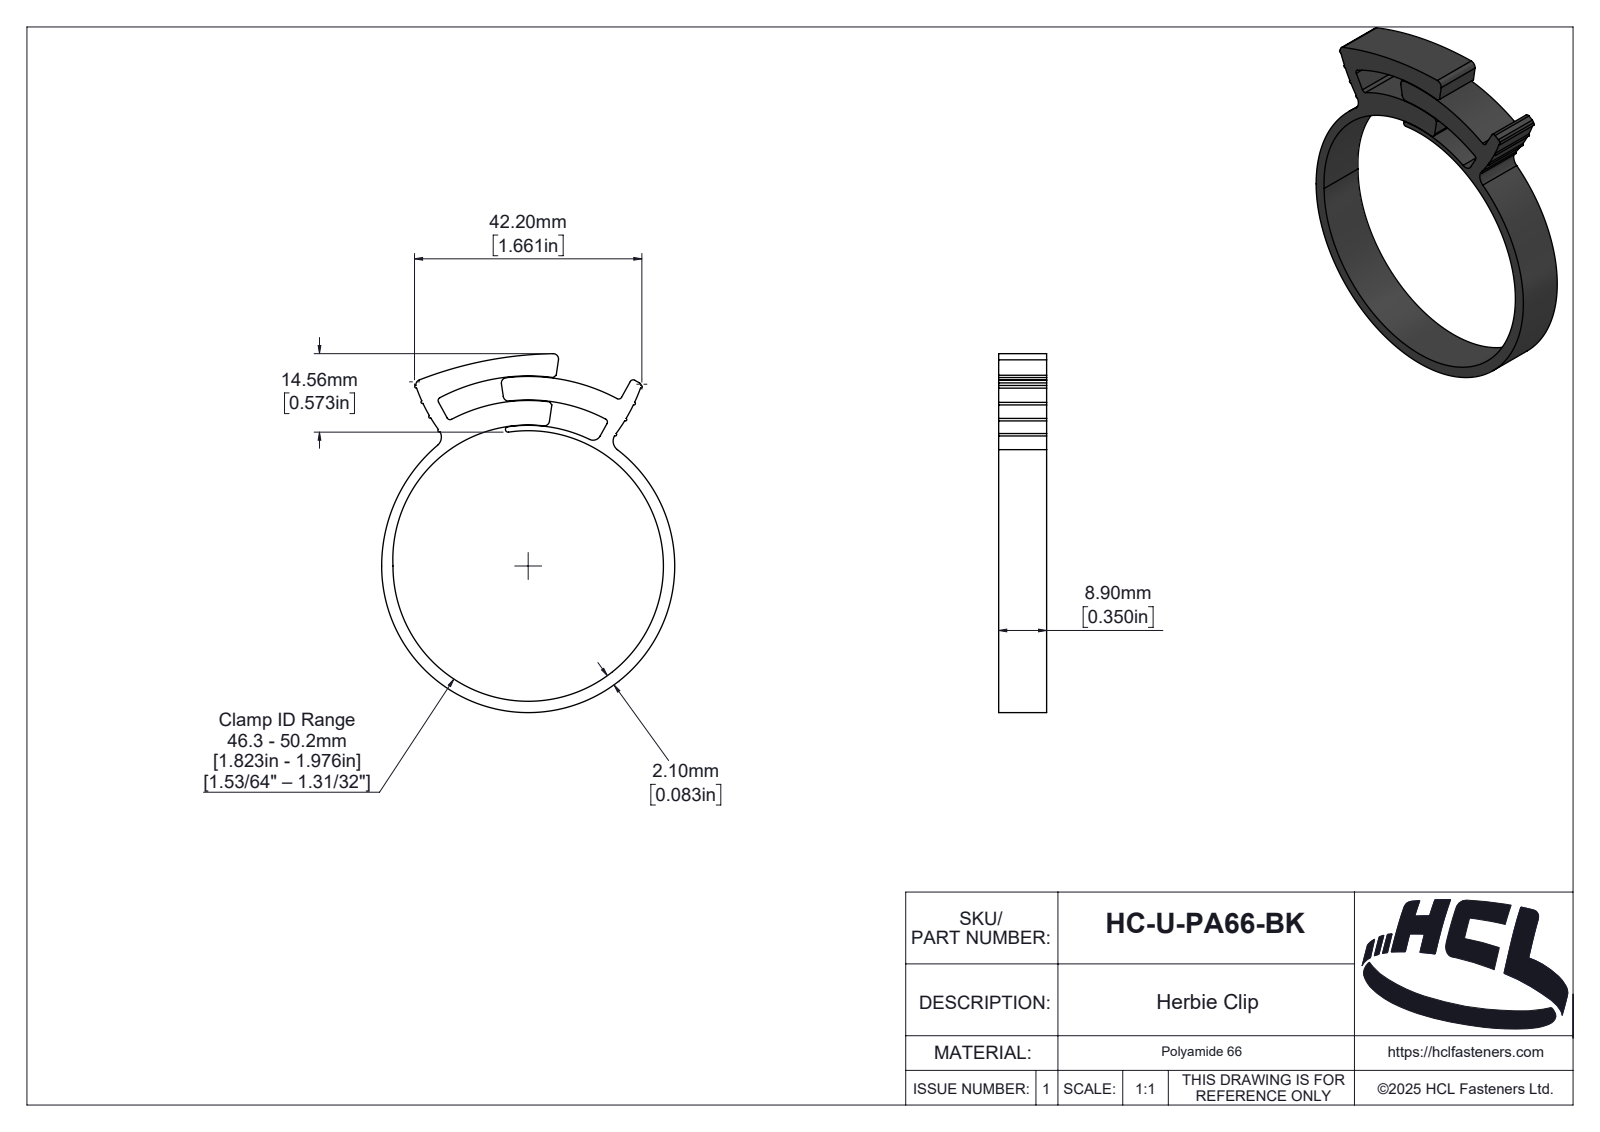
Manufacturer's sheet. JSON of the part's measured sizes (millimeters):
{"part_name": "HC-U-PA66-BK", "step_written_by": "SolidWorks 2025 (AUTOMOTIVE_DESIGN)", "units": "millimeters", "bodies": {"solids": 1, "faces": 162, "planar": 13, "cylindrical": 100, "other": 49}, "overall_size": [66.59, 54.4, 8.9], "volume_mm3": 5670, "surface_area_mm2": 5619, "partial_cylinders_radius": [[0.25, 8], [0.6, 6], [1, 5], [2, 2], [0.17, 1], [0.5, 1], [0.67, 1], [0.84, 1]], "face_to_face_distances": [8.9]}
